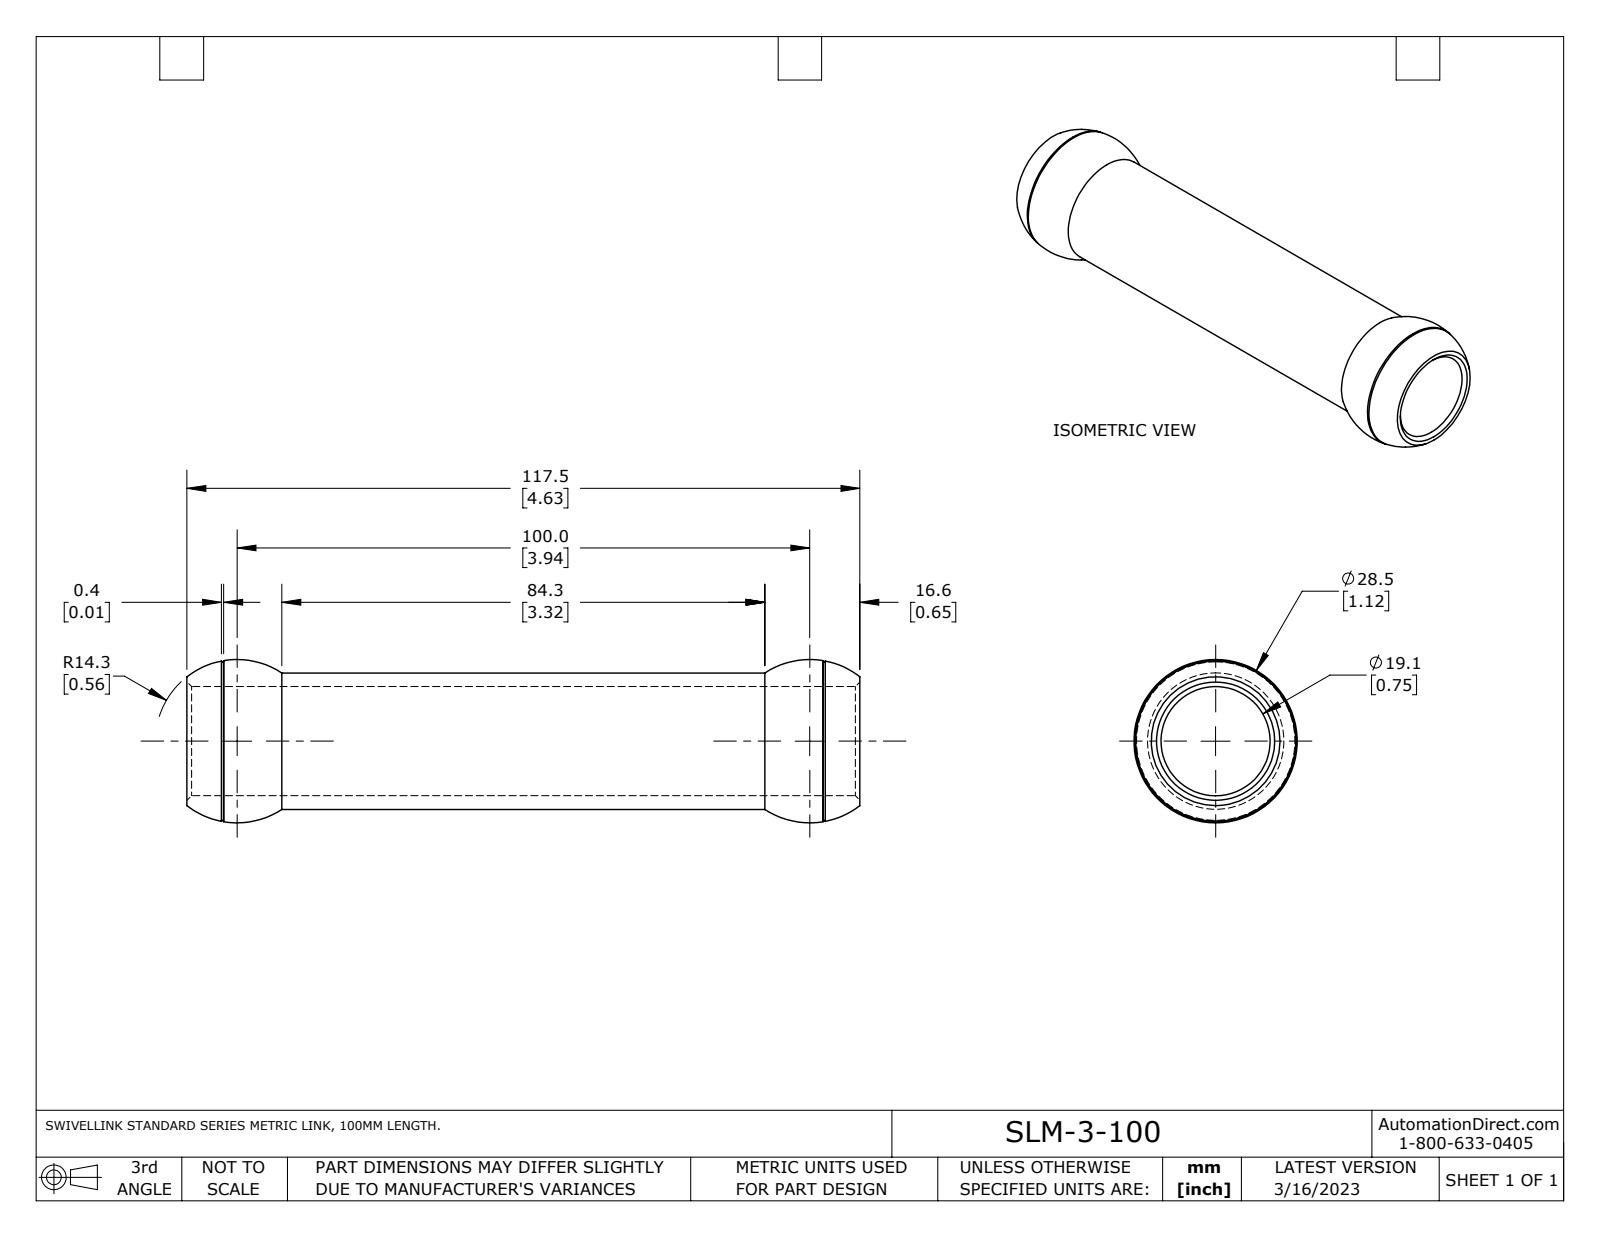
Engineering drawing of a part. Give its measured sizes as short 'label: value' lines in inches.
name: SLM-3-100
written by: SolidWorks 2021 (AUTOMOTIVE_DESIGN)
unit: in
bodies: 2 solids, 14 faces (2 planar, 2 cylindrical, 10 other)
size: 5.059 × 1.107 × 1.107
volume: 4.291 in³; area: 27.86 in²
bosses: 1× ⌀0.937, 1× ⌀0.75
face distances: 4.626
